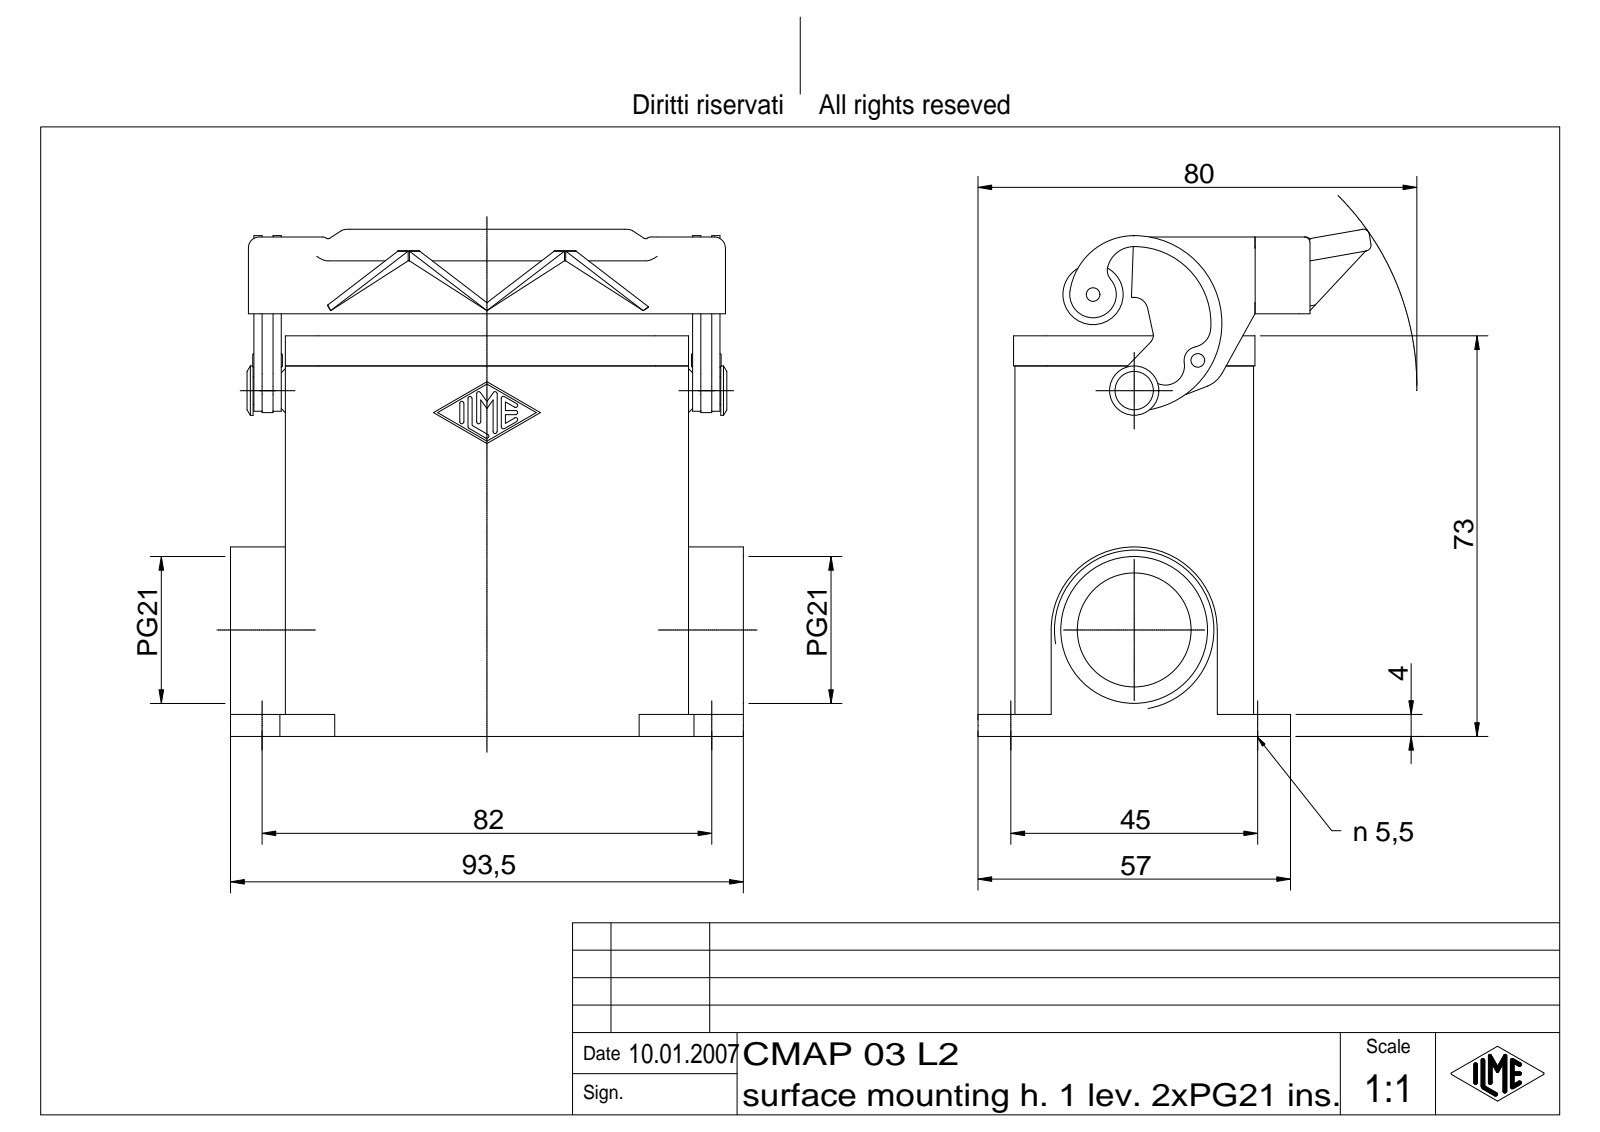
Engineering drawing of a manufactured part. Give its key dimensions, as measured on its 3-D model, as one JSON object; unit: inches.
{"part_name": "CMAP 03 L2", "step_written_by": "Autodesk Inventor 7 (AUTOMOTIVE_DESIGN)", "units": "inches", "bodies": {"solids": 4, "faces": 432, "planar": 164, "cylindrical": 123, "other": 145}, "overall_size": [3.681, 3.639, 2.823], "volume_in3": 6.32, "surface_area_in2": 83.01, "round_holes": [[0.217, 4], [0.079, 1], [0.818, 1], [1.054, 1]], "round_bosses_or_shafts": [[0.433, 1], [0.354, 1], [0.197, 1], [0.118, 1], [0.098, 1]], "partial_cylinders_radius": [[0.015, 14], [0.079, 12], [0.236, 8], [0.039, 7], [0.059, 5], [0.118, 4], [0.098, 3], [0.138, 2]], "face_to_face_distances": [0.118, 1.594, 0.157, 1.713, 1.476, 0.463, 2.657, 2.431, 0.344, 2.5], "hole_center_spacings": [1.772, 3.228, 3.683, 1.987]}
